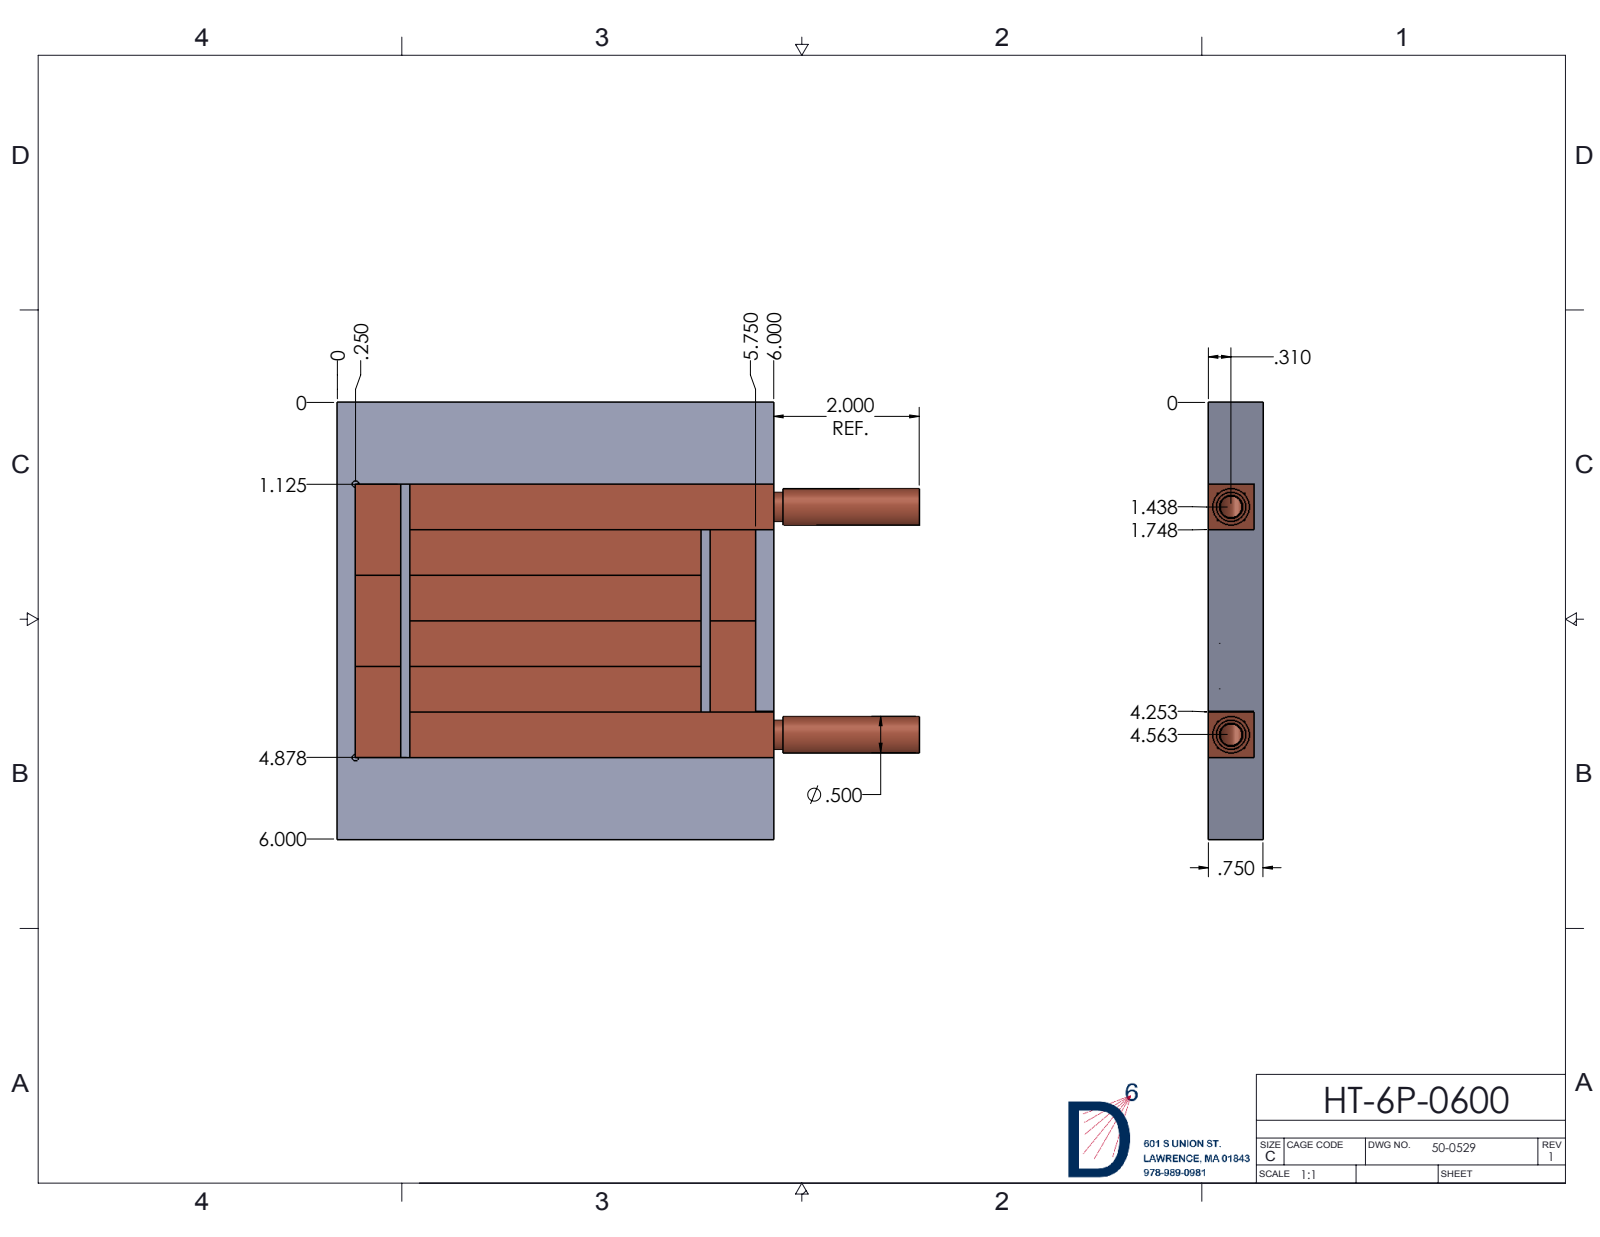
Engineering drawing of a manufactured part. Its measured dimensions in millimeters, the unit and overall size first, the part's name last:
Units: millimetres
Overall size (bounding box): 203.2 × 152.4 × 19.1
Round holes (diameter × count): ⌀7.6 ×6, ⌀8.1 ×2, ⌀10.2 ×2, ⌀10.2 ×2
Round bosses / shafts (diameter × count): ⌀12.7 ×2, ⌀10.9 ×2
Main face-to-face distances: 19.1, 31.8, 3.3, 15.7, 12.7, 63.5, 15.9, 15.9, 3.2, 44.5
Hole centre spacings: 31.8, 15.9, 15.9, 47.6, 63.5, 47.6, 79.4, 123.8
Volume: 379 400 mm³ · Surface area: 172 500 mm²
Bodies: 21 solids, 293 faces (243 planar, 50 cylindrical, 0 other)
Part name (STEP PRODUCT): HT-SIDEBYSIDE-CONNECTOR; ST-CONN-4.0; SIDEBYSIDE-FILLER-S; BP-6P-0600 (+4 more)
STEP written by: SolidWorks 2018 (CONFIG_CONTROL_DESIGN)
